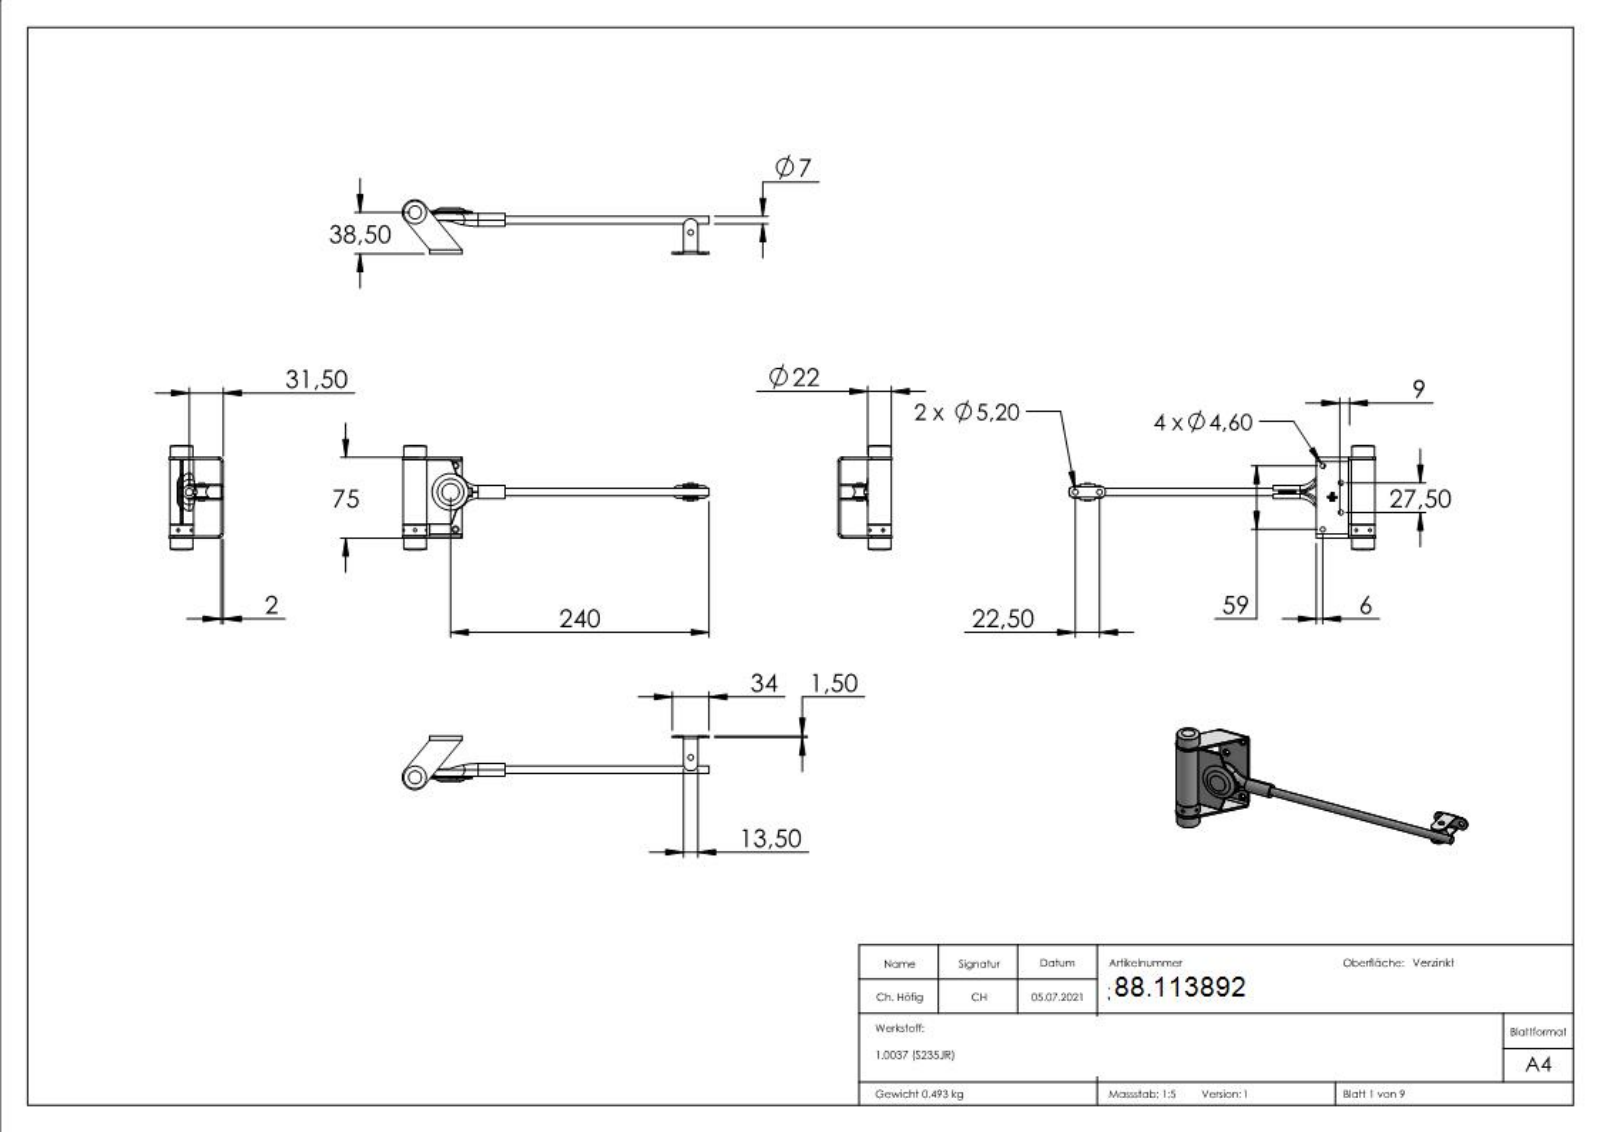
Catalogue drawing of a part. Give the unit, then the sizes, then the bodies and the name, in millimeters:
Units: millimetres
Overall size (bounding box): 284.5 × 97 × 50
Round holes (diameter × count): ⌀3 ×6, ⌀4.6 ×4, ⌀5.2 ×2, ⌀7 ×1, ⌀10 ×1
Round bosses / shafts (diameter × count): ⌀22 ×1, ⌀21 ×1, ⌀13 ×1, ⌀12 ×1, ⌀5.2 ×1, ⌀2.8 ×1
Partial cylindrical surfaces — rounded edges, fillets, slot ends (radius × count): R0.2 ×25, R0.5 ×17, R2 ×8, R1 ×2, R2.5 ×2, R4 ×2, R5.85 ×2, R21.02 ×2
Main face-to-face distances: 2, 37.5, 73, 35.5, 75, 71, 1.5, 39.5, 2.33, 72.67
Hole centre spacings: 23.07, 46.42, 22.5, 26.37, 27.5, 37.51, 48.53, 59
Volume: 63 215 mm³ · Surface area: 36 616 mm²
Bodies: 9 solids, 598 faces (219 planar, 142 cylindrical, 237 other)
Part name (STEP PRODUCT): 3892; 389x Teil5; 389x Teil2_389x Teil2; 389x Teil2 (+8 more)
STEP written by: SolidWorks 2018 (CONFIG_CONTROL_DESIGN)
